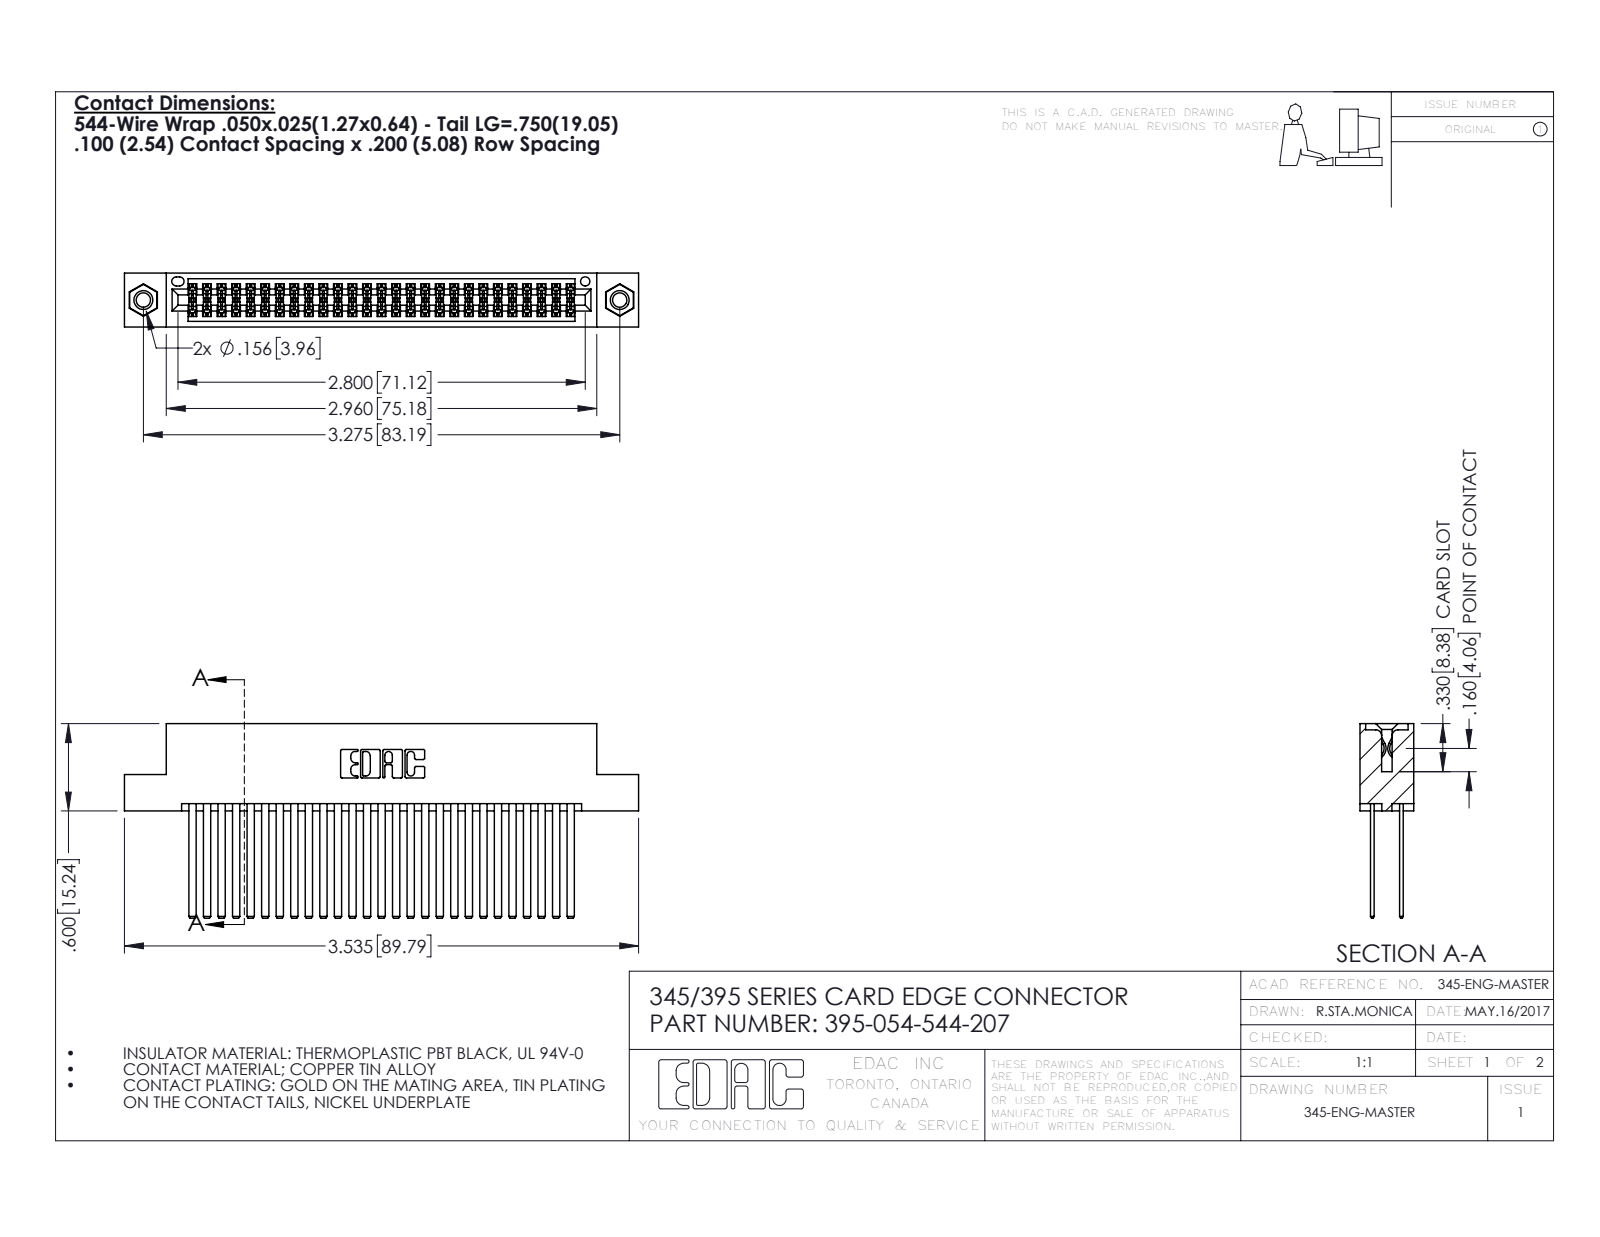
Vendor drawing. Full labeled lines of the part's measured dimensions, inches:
Part name (STEP PRODUCT): 345-250-001_345-250-005-103; 395-054-544-207; 345-292-001_345-293-144; 345 Part_Flush Mounting Lugs - 0.156 Dia-TI
STEP written by: SolidWorks 2016 (CONFIG_CONTROL_DESIGN)
Units: inches
Bodies: 57 solids, 2562 faces (1678 planar, 868 cylindrical, 16 other)
Overall size (bounding box): 3.535 × 1.337 × 0.37
Volume: 0.569 in³ · Surface area: 24.4 in²
Round holes (diameter × count): ⌀0.098 ×2, ⌀0.125 ×2, ⌀0.156 ×2, ⌀0.064 ×1
Round bosses / shafts (diameter × count): ⌀0.155 ×2
Partial cylindrical surfaces — rounded edges, fillets, slot ends (radius × count): R0.006 ×81, R0.01 ×22, R0.007 ×6, R0.031 ×6, R0.026 ×3, R0.014 ×2, R0.019 ×2, R0.022 ×2
Main face-to-face distances: 0.2, 0.072, 0.298, 0.025, 0.098, 0.272, 0.225, 0.175, 0.37, 0.05
Hole centre spacings: 0.27, 3.04, 3.275
